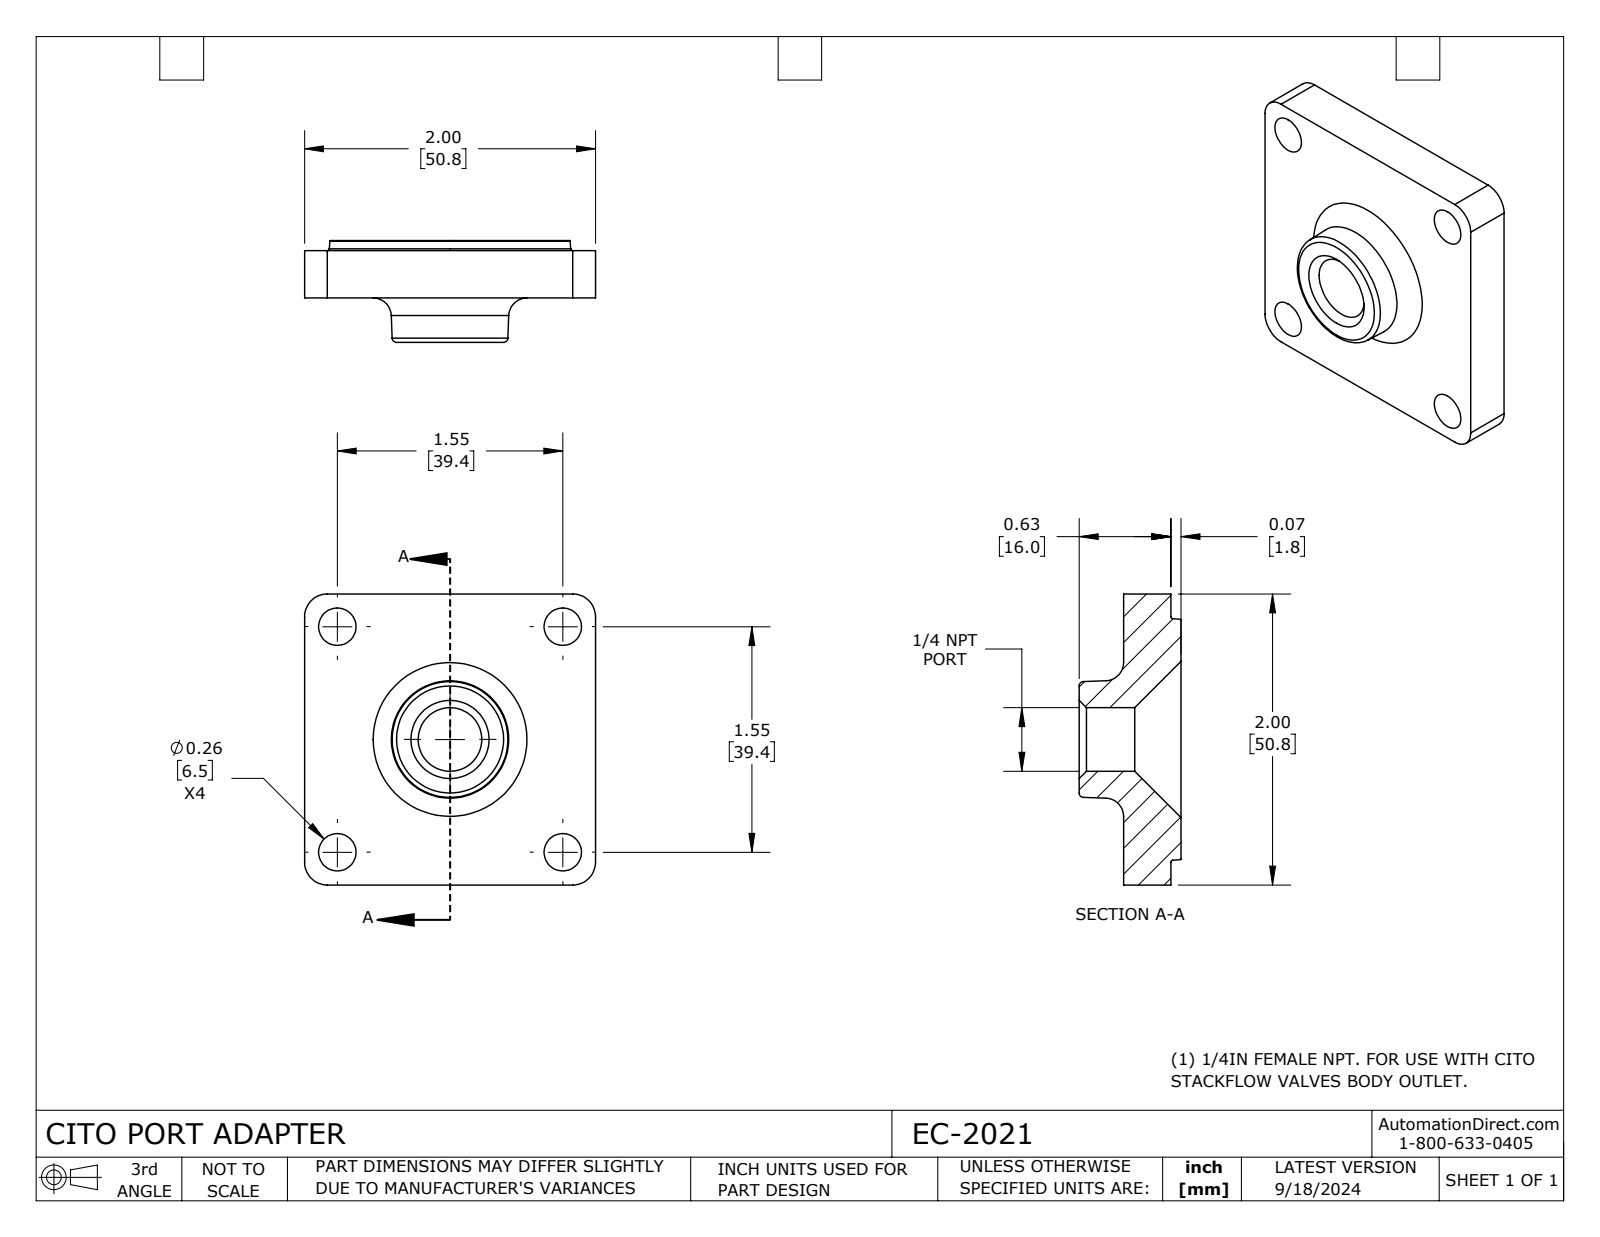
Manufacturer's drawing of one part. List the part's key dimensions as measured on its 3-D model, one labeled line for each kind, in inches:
Part name (STEP PRODUCT): EC-2021
STEP written by: SolidWorks 2023 (CONFIG_CONTROL_DESIGN)
Units: inches
Bodies: 1 solid, 38 faces (8 planar, 14 cylindrical, 16 other)
Overall size (bounding box): 2 × 2 × 0.7
Volume: 1.33 in³ · Surface area: 12.5 in²
Round holes (diameter × count): ⌀0.257 ×4, ⌀0.437 ×1
Partial cylindrical surfaces — rounded edges, fillets, slot ends (radius × count): R0.156 ×4
Main face-to-face distances: 0.325, 0.395, 0.07, 2, 0.305, 0.63, 0.7
Hole centre spacings: 1.096, 1.55, 2.191
